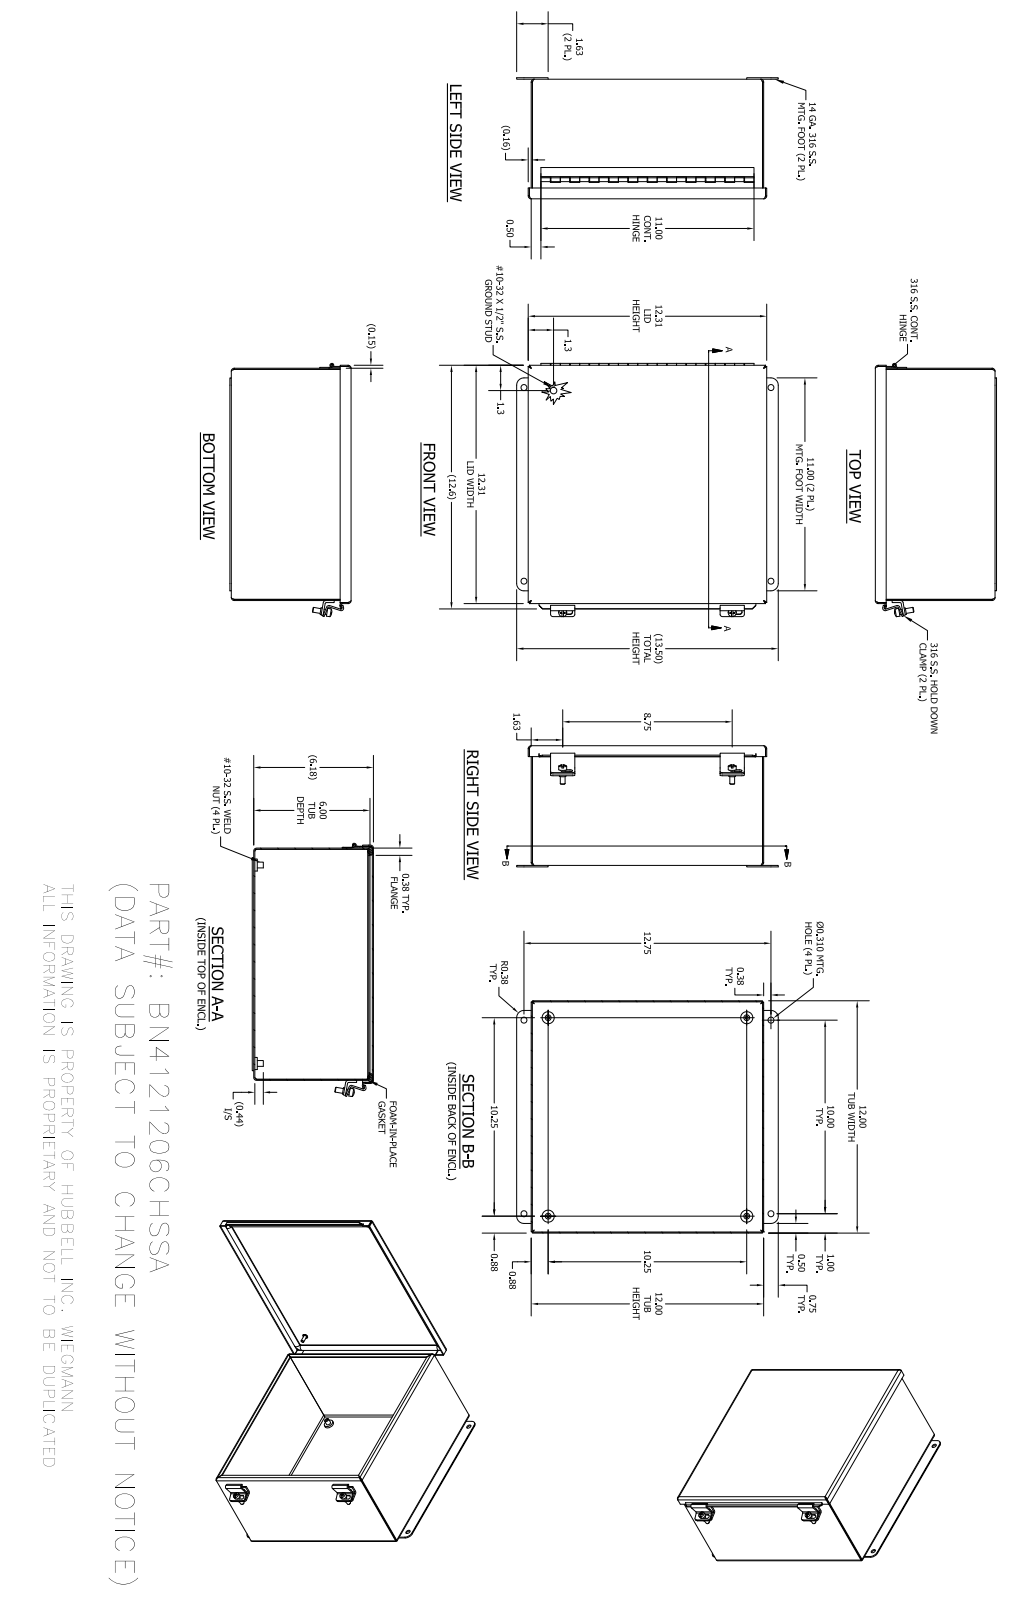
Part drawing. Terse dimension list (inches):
name: B_121206_SSABKP; 32884LH; 32884P; 32884TH (+8 more)
written by: Autodesk Inventor 2016 (AUTOMOTIVE_DESIGN)
unit: in
bodies: 19 solids, 468 faces (256 planar, 145 cylindrical, 67 other)
size: 13.5 × 13.086 × 6.256
volume: 44.53 in³; area: 1 428 in²
holes: 4× ⌀0.11, 4× ⌀0.156, 4× ⌀0.31, 2× ⌀0.196, 1× ⌀0.117
bosses: 4× ⌀0.625, 4× ⌀0.3, 2× ⌀0.409, 2× ⌀0.344, 2× ⌀0.25, 1× ⌀0.337, 1× ⌀0.2, 1× ⌀0.19
rounds: 13× R0.094, 13× R0.153, 8× R0.066, 8× R0.125, 4× R0.133, 4× R0.228, 4× R0.375, 3× R0.063
face distances: 0.059, 6.122, 11.941, 6.181, 6.063, 12, 11.882, 5.941, 0.181, 0.075
hole spacings: 1.256, 8.75, 10.202, 10.25, 11.5, 15.322, 0.75, 10
